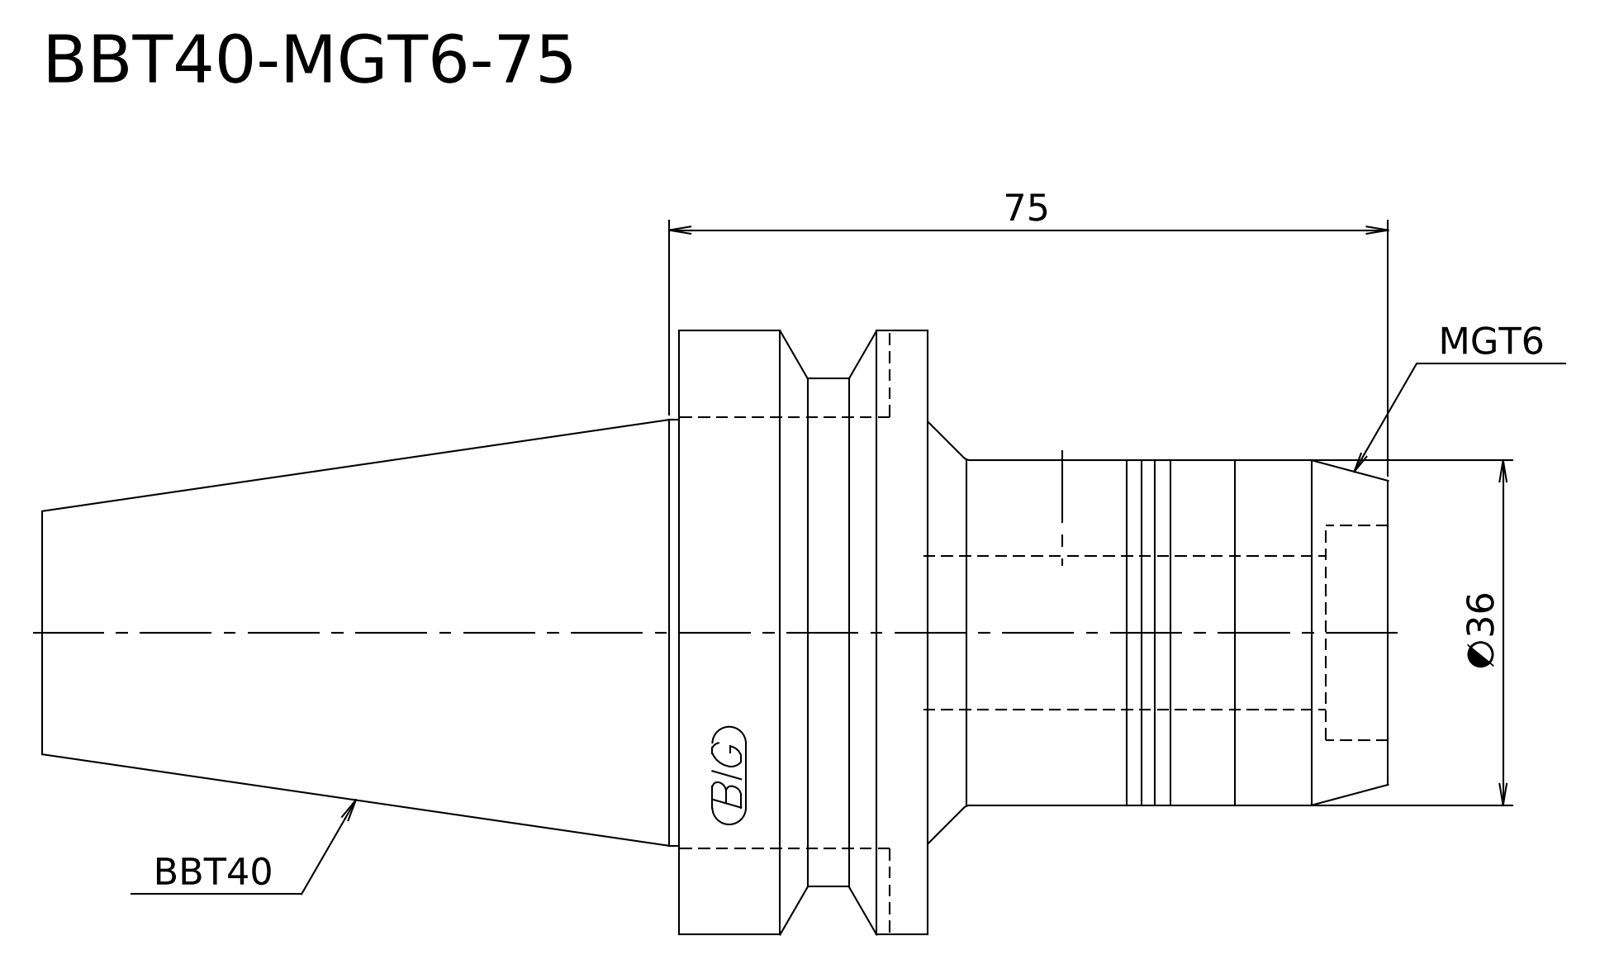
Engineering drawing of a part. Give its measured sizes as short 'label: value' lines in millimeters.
written by: Kubotek KeyCreator V8.5.1 (14335) (CONFIG_CONTROL_DESIGN)
unit: mm
bodies: 1 solid, 14 faces (4 planar, 5 cylindrical, 5 other)
size: 140.4 × 63 × 63
volume: 189 108 mm³; area: 23 484 mm²
bosses: 1× ⌀63, 1× ⌀53, 1× ⌀44.45, 1× ⌀36
face distances: 26, 48, 74, 140.4, 92.4, 66.4
